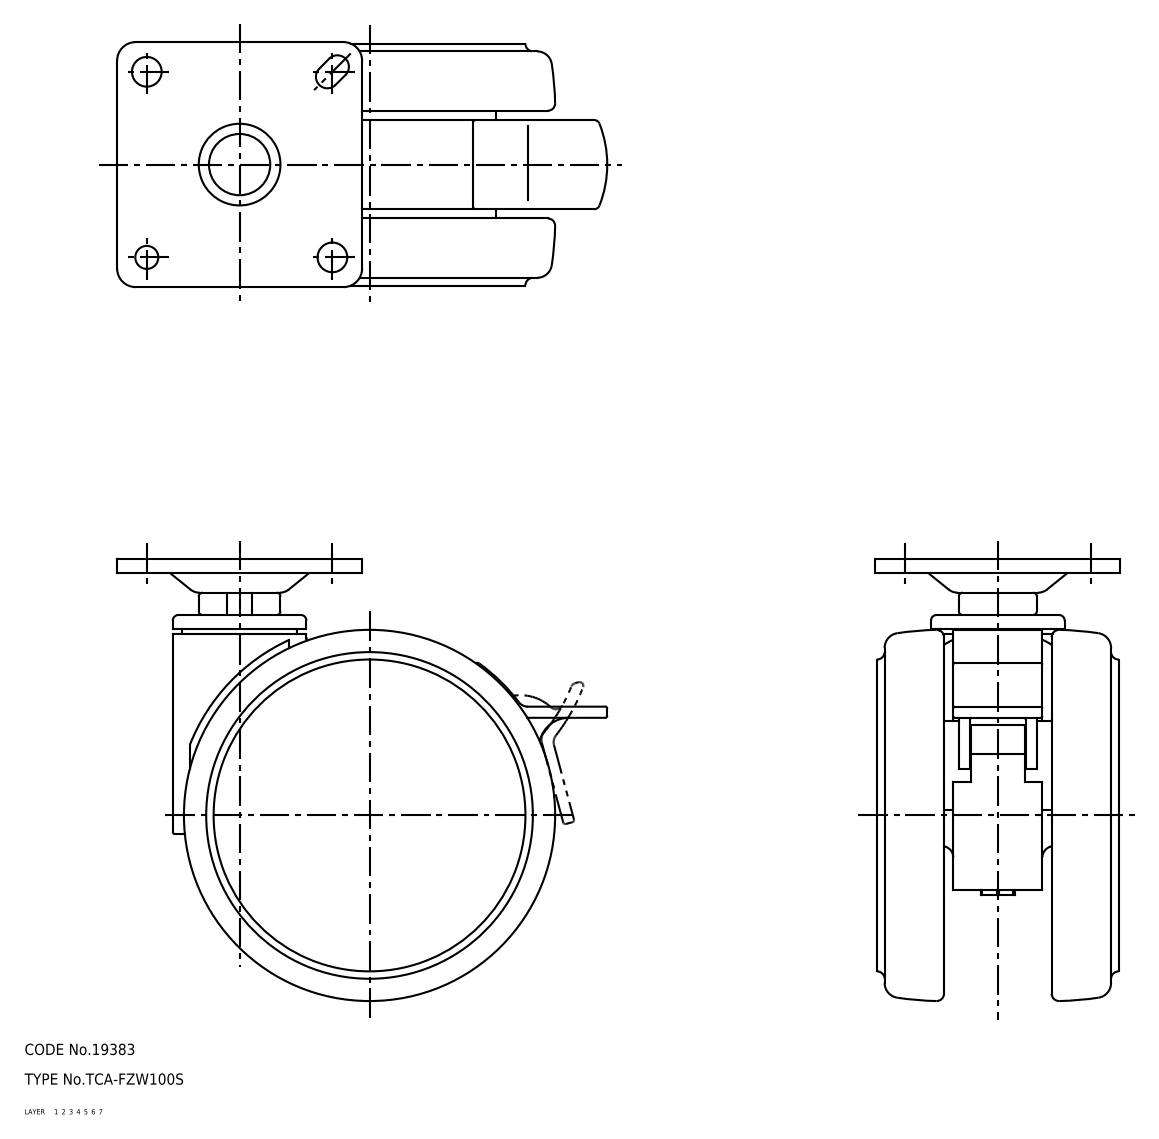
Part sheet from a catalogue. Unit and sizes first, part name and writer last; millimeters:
Units: millimetres
Overall size (bounding box): 132.03 × 119 × 66
Round holes (diameter × count): ⌀8 ×2, ⌀2.8 ×1, ⌀3 ×1, ⌀3.3 ×1, ⌀4.1 ×1, ⌀4.2 ×1, ⌀6 ×1, ⌀6.2 ×1, ⌀9.1 ×1, ⌀10 ×1, ⌀10.1 ×1, ⌀10.5 ×1
Round bosses / shafts (diameter × count): ⌀87.8 ×1, ⌀36 ×1, ⌀31 ×1, ⌀27.9 ×1, ⌀27.6 ×1, ⌀22 ×1, ⌀20 ×1, ⌀19 ×1
Partial cylindrical surfaces — rounded edges, fillets, slot ends (radius × count): R0.5 ×236, R1.2 ×160, R1 ×87, R2 ×25, R1.5 ×23, R0.2 ×18, R0.3 ×12, R3 ×8
Main face-to-face distances: 1.8, 61.6, 63.4, 3.6, 59.8, 14.5, 16.3, 45.3, 18.1, 47.1
Hole centre spacings: 35.36, 50, 22.78, 29.45, 44, 70.71
Volume: 318 166 mm³ · Surface area: 133 654 mm²
Bodies: 1 solid, 2528 faces (874 planar, 1205 cylindrical, 449 other)
Part name (STEP PRODUCT): caster; TCA-FZW100S
STEP written by: SolidWorks 2015 (AUTOMOTIVE_DESIGN)
